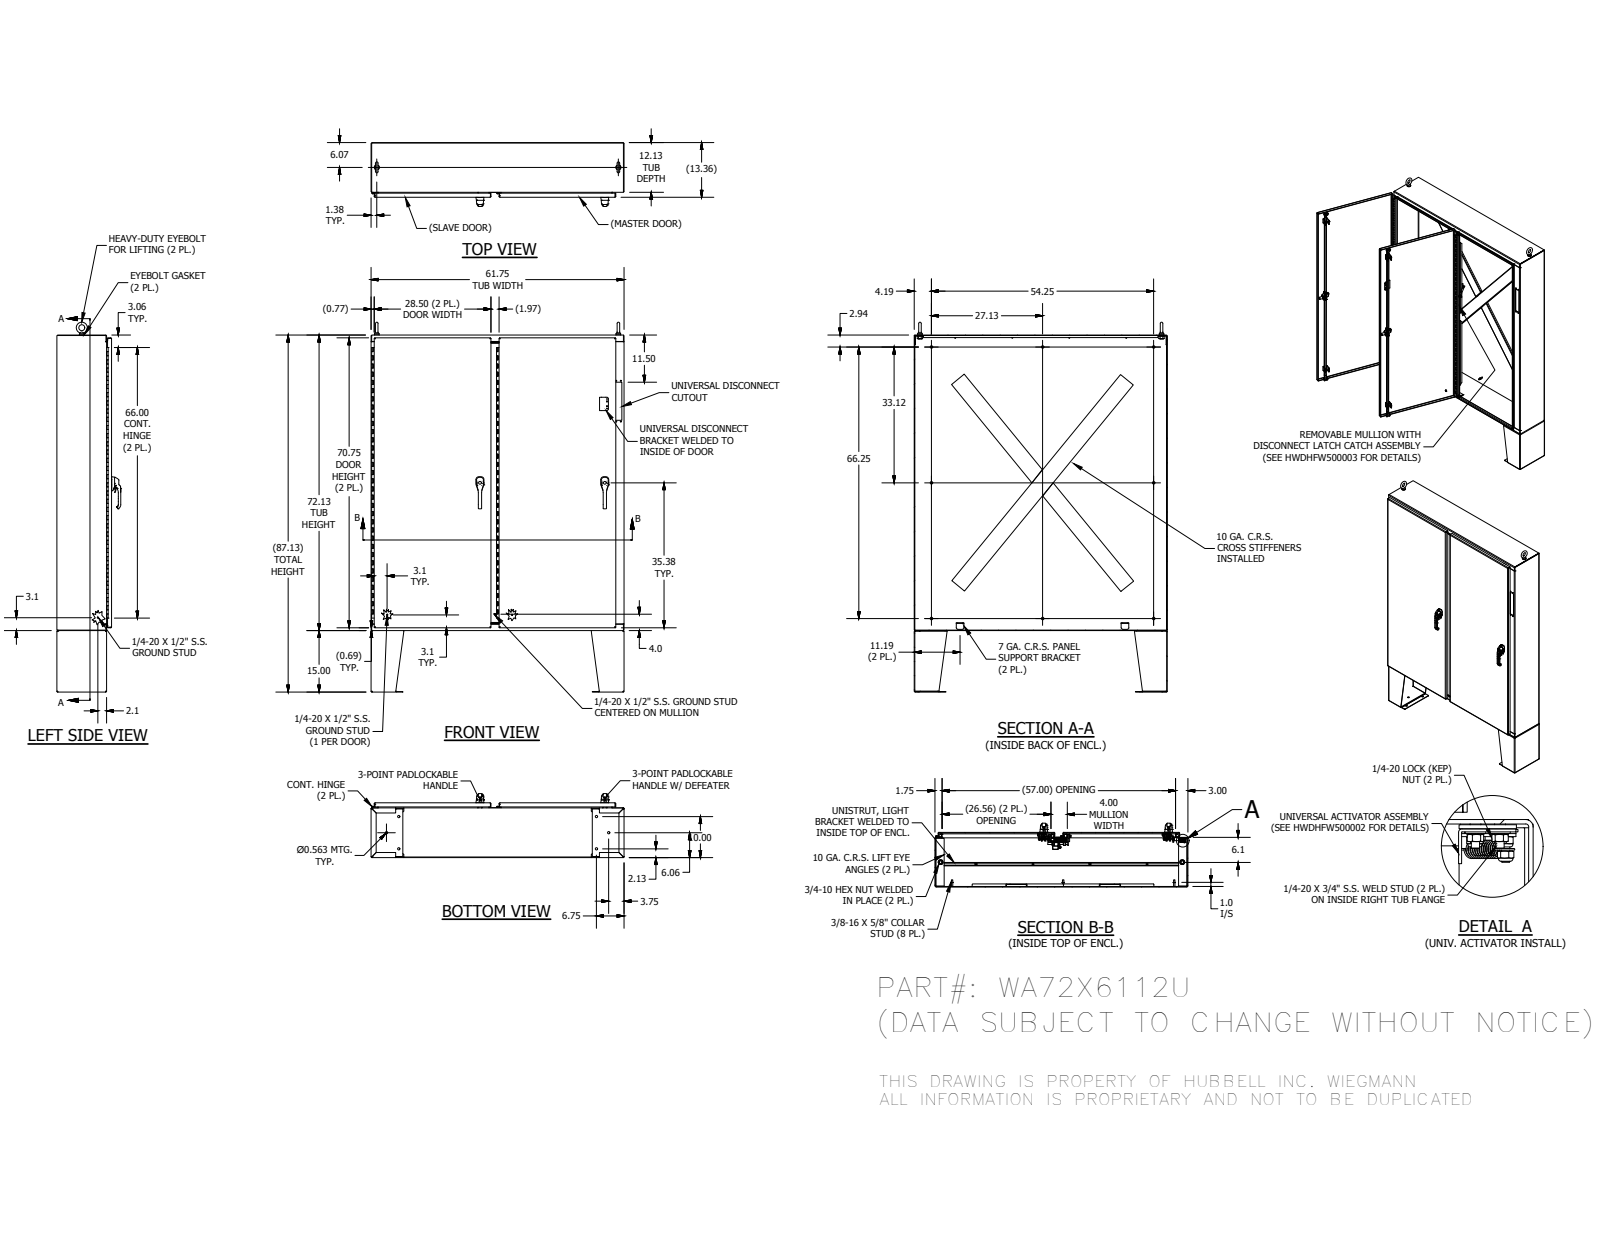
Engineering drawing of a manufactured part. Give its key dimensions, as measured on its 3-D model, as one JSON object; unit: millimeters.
{"part_name": "WA72X6112UBLR; WAX6112UTOP; WAX6112UBTM; HFW332010S (+8 more)", "step_written_by": "Autodesk Inventor 2016 (AUTOMOTIVE_DESIGN)", "units": "millimeters", "bodies": {"solids": 215, "faces": 8901, "planar": 4144, "cylindrical": 2996, "other": 1761}, "overall_size": [2292.29, 1568.45, 396.45], "volume_mm3": 34780000, "surface_area_mm2": 21330000, "round_holes": [[6.35, 18], [9.52, 18], [14.29, 18], [4.83, 8], [5.08, 8], [5.16, 8], [7.02, 8], [7.33, 8], [7.94, 8], [8.51, 8], [9.65, 8], [5.11, 7]], "round_bosses_or_shafts": [[6.35, 23], [8.38, 18], [15.88, 13], [8.56, 12], [9.52, 11], [14.29, 9], [25.4, 8], [11.13, 8]], "partial_cylinders_radius": [[0.5, 339], [0.3, 202], [0.51, 192], [0.47, 44], [2.38, 41], [1.27, 40], [3.17, 37], [2, 27]], "face_to_face_distances": [3.4, 335.7, 332.3, 339.1, 3.41, 1565.04, 1828.57, 304.57, 3.18, 31.13], "hole_center_spacings": [774.7, 0.77, 0.78, 27.99, 28, 50.8, 43.45, 775.03]}
